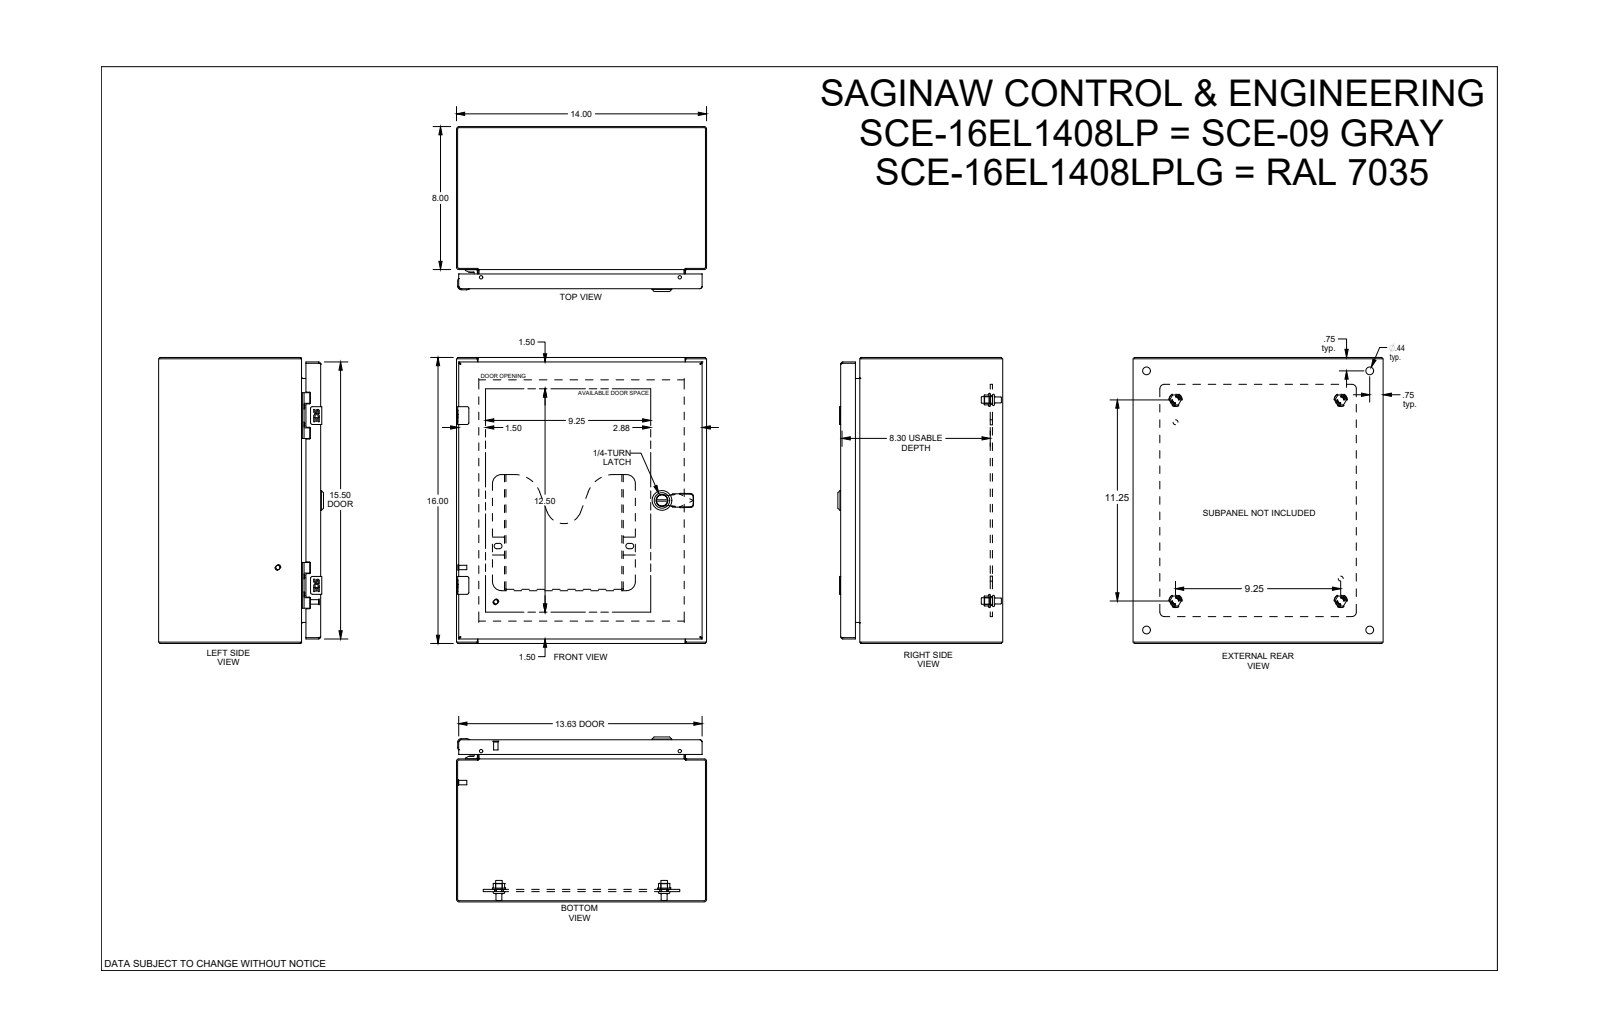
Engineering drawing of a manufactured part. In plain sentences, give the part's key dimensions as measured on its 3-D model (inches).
The part is named "SCE-16EL1408LP". Its 3-D file was written by "SolidWorks 2019 (AUTOMOTIVE_DESIGN)". It is 42 solids with 2221 faces: 1015 planar, 558 cylindrical and 648 other. Overall it measures 16 by 14 by 9.23 inches. Its volume is 109.3 cubic inches and its surface area 2 685 square inches. Round holes: 4 of diameter 0.172, 4 of diameter 0.205, 4 of diameter 0.244, 4 of diameter 0.266, 4 of diameter 0.367, 4 of diameter 0.375, 4 of diameter 0.437, 4 of diameter 0.5, 2 of diameter 0.04, 2 of diameter 0.188, 2 of diameter 0.218, 2 of diameter 0.25. Round bosses or shafts: 6 of diameter 0.17, 4 of diameter 0.366, 4 of diameter 0.332, 4 of diameter 0.25, 4 of diameter 0.248, 4 of diameter 0.24, 3 of diameter 0.196, 2 of diameter 0.563. Partial cylindrical surfaces (rounded edges, fillets, slot ends): 30 of radius 0.012, 28 of radius 0.01, 24 of radius 0.015, 17 of radius 0.04, 13 of radius 0.06, 12 of radius 0.02, 12 of radius 0.029, 12 of radius 0.1. The main face-to-face distances are 0.075, 0.075, 0.06, 13.925, 15.925, 9.073, 8.998, 9.013, 8.938, 0.125. The hole center spacings are 0.985, 9.5, 0.02, 0.493, 0.494, 2.298, 2.993, 10.996.
